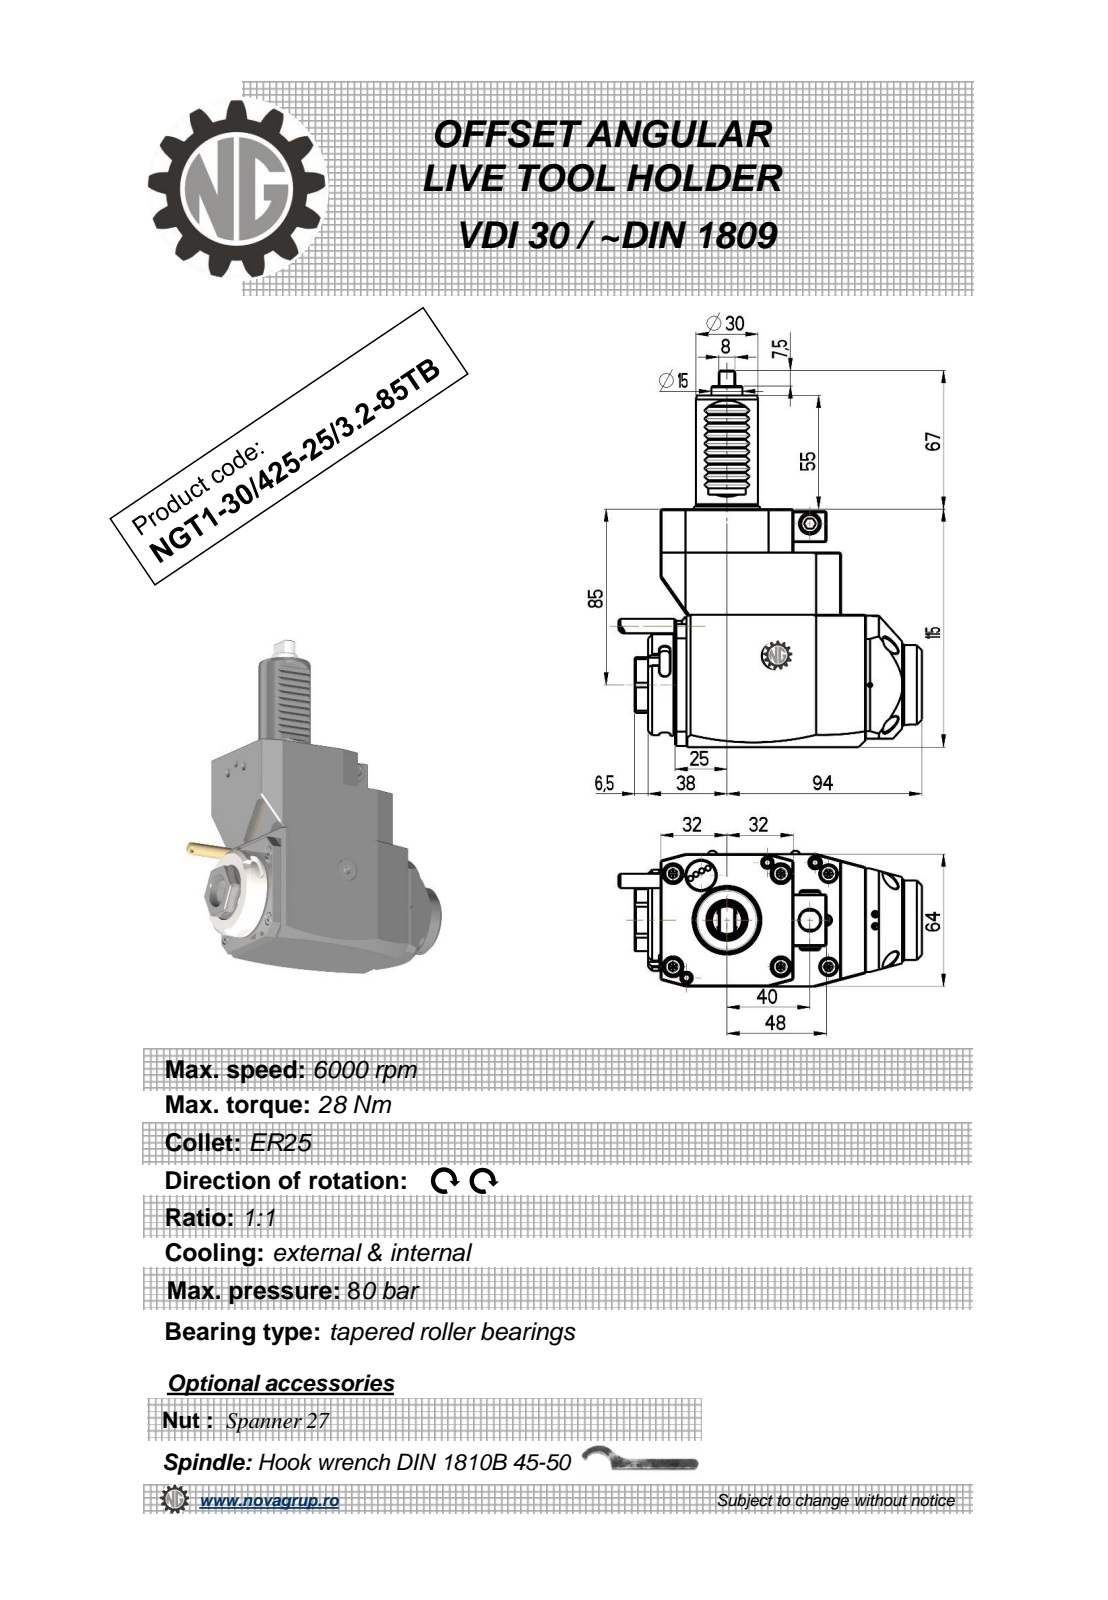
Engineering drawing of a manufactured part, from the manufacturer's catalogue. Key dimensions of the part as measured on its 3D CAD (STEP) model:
Part name (STEP PRODUCT): NGT1_30_425_25_3_2_85TB
STEP written by: PRO/ENGINEER BY PARAMETRIC TECHNOLOGY CORPORATION, 2010280 (CONFIG_CONTROL_DESIGN)
Units: millimetres
Bodies: 1 solid, 346 faces (198 planar, 74 cylindrical, 74 other)
Overall size (bounding box): 182 × 146.38 × 64
Volume: 723 478 mm³ · Surface area: 60 421 mm²
Round holes (diameter × count): ⌀2.5 ×1, ⌀3 ×1, ⌀8.5 ×1, ⌀9.5 ×1, ⌀10 ×1, ⌀18 ×1
Round bosses / shafts (diameter × count): ⌀8.96 ×2, ⌀49 ×1, ⌀42 ×1, ⌀38.5 ×1, ⌀30 ×1, ⌀15 ×1, ⌀10 ×1, ⌀7 ×1
Partial cylindrical surfaces — rounded edges, fillets, slot ends (radius × count): R0.3 ×10, R2.5 ×6, R0.8 ×2, R180 ×2, R4.5 ×1, R7.2 ×1, R15 ×1, R21.5 ×1
Main face-to-face distances: 64, 115, 7, 80, 87, 6, 21, 94, 12.5, 13
Hole centre spacings: 34.25, 51.62, 76.5
